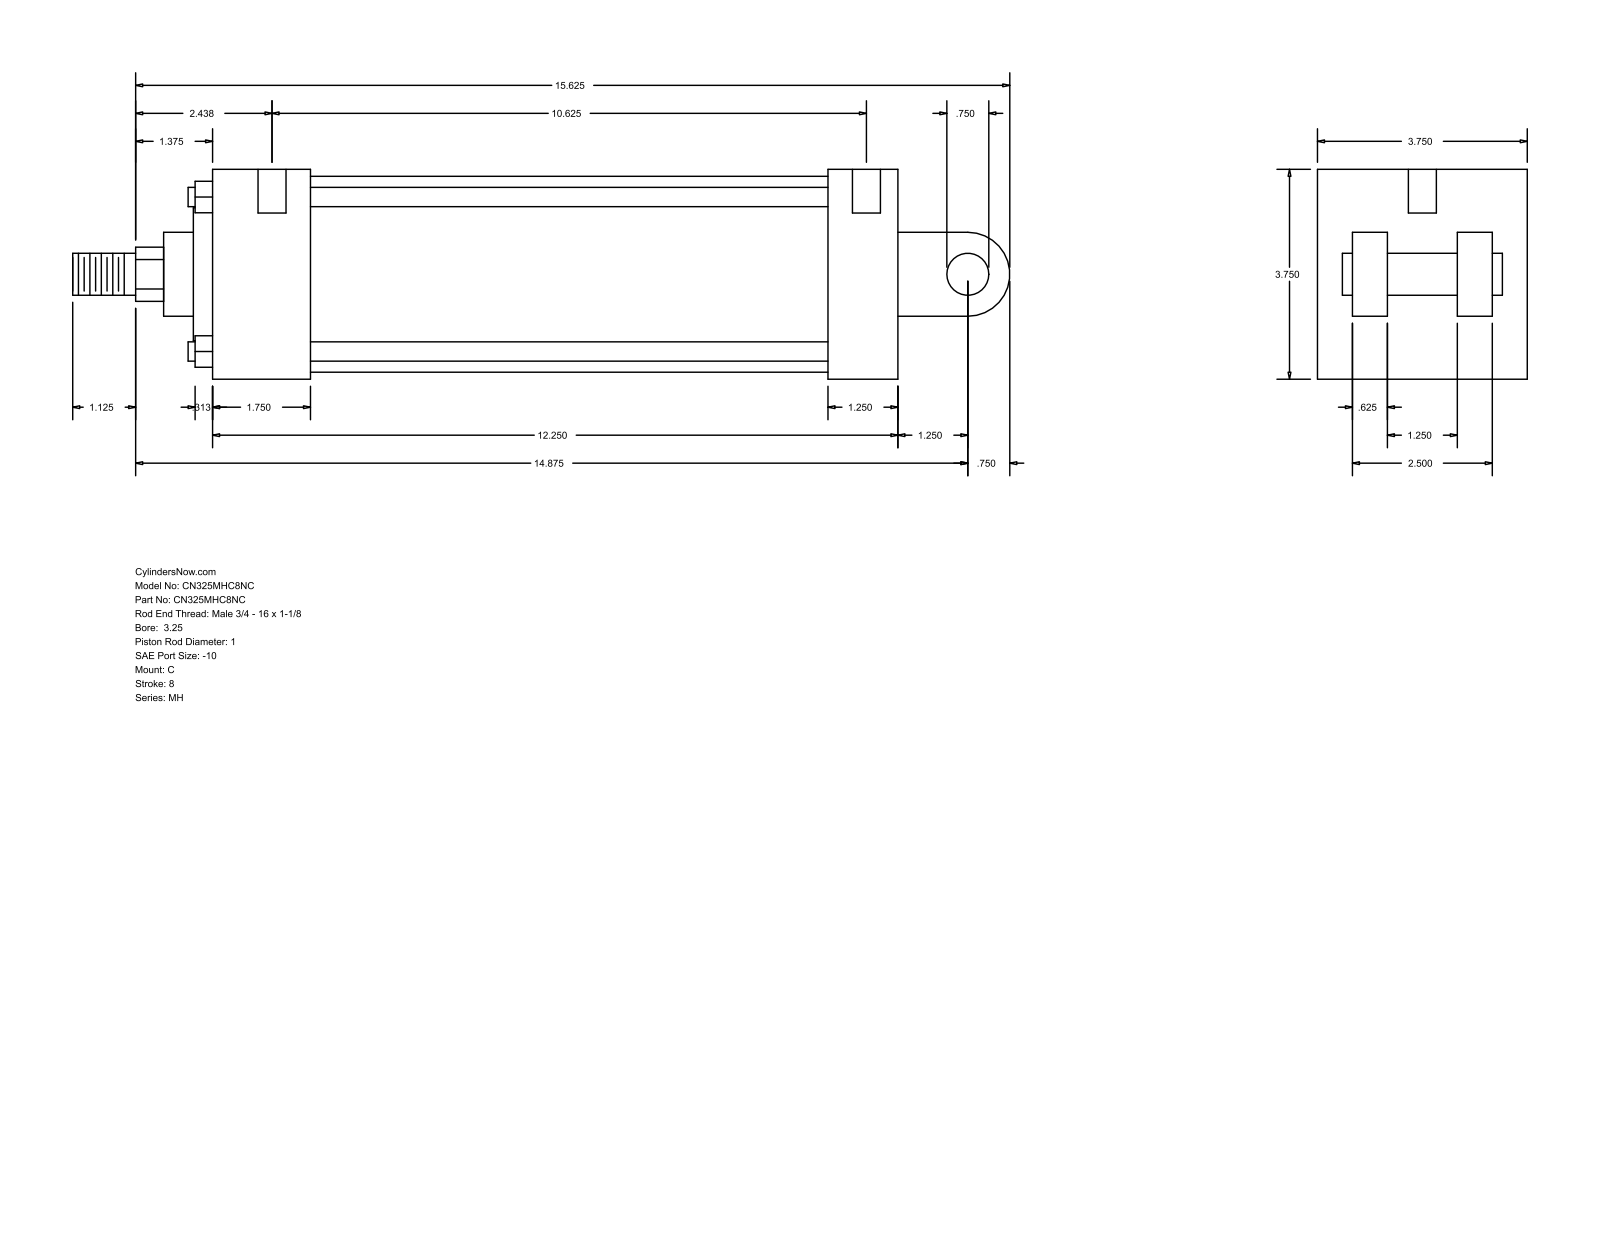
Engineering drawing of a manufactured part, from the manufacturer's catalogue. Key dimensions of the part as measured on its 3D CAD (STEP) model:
Part name (STEP PRODUCT): MH_C__0325_1
STEP written by: GSSL Pune (CONFIG_CONTROL_DESIGN)
Units: millimetres
Bodies: 0 solids, 101 faces (71 planar, 30 cylindrical, 0 other)
Overall size (bounding box): 425.45 × 95.25 × 95.25
Round holes (diameter × count): ⌀5.56 ×4, ⌀12.7 ×2
Round bosses / shafts (diameter × count): ⌀8.76 ×4, ⌀19.05 ×2, ⌀88.9 ×1, ⌀60.33 ×1, ⌀38.1 ×1, ⌀25.4 ×1
Partial cylindrical surfaces — rounded edges, fillets, slot ends (radius × count): R12.29 ×1, R19.05 ×1
Main face-to-face distances: 95.24, 15.87, 311.15, 63.5, 79.37, 31.74, 47.63, 44.46, 279.4, 234.94
Hole centre spacings: 276.22, 1.58, 4.76, 269.88, 271.46, 274.64
